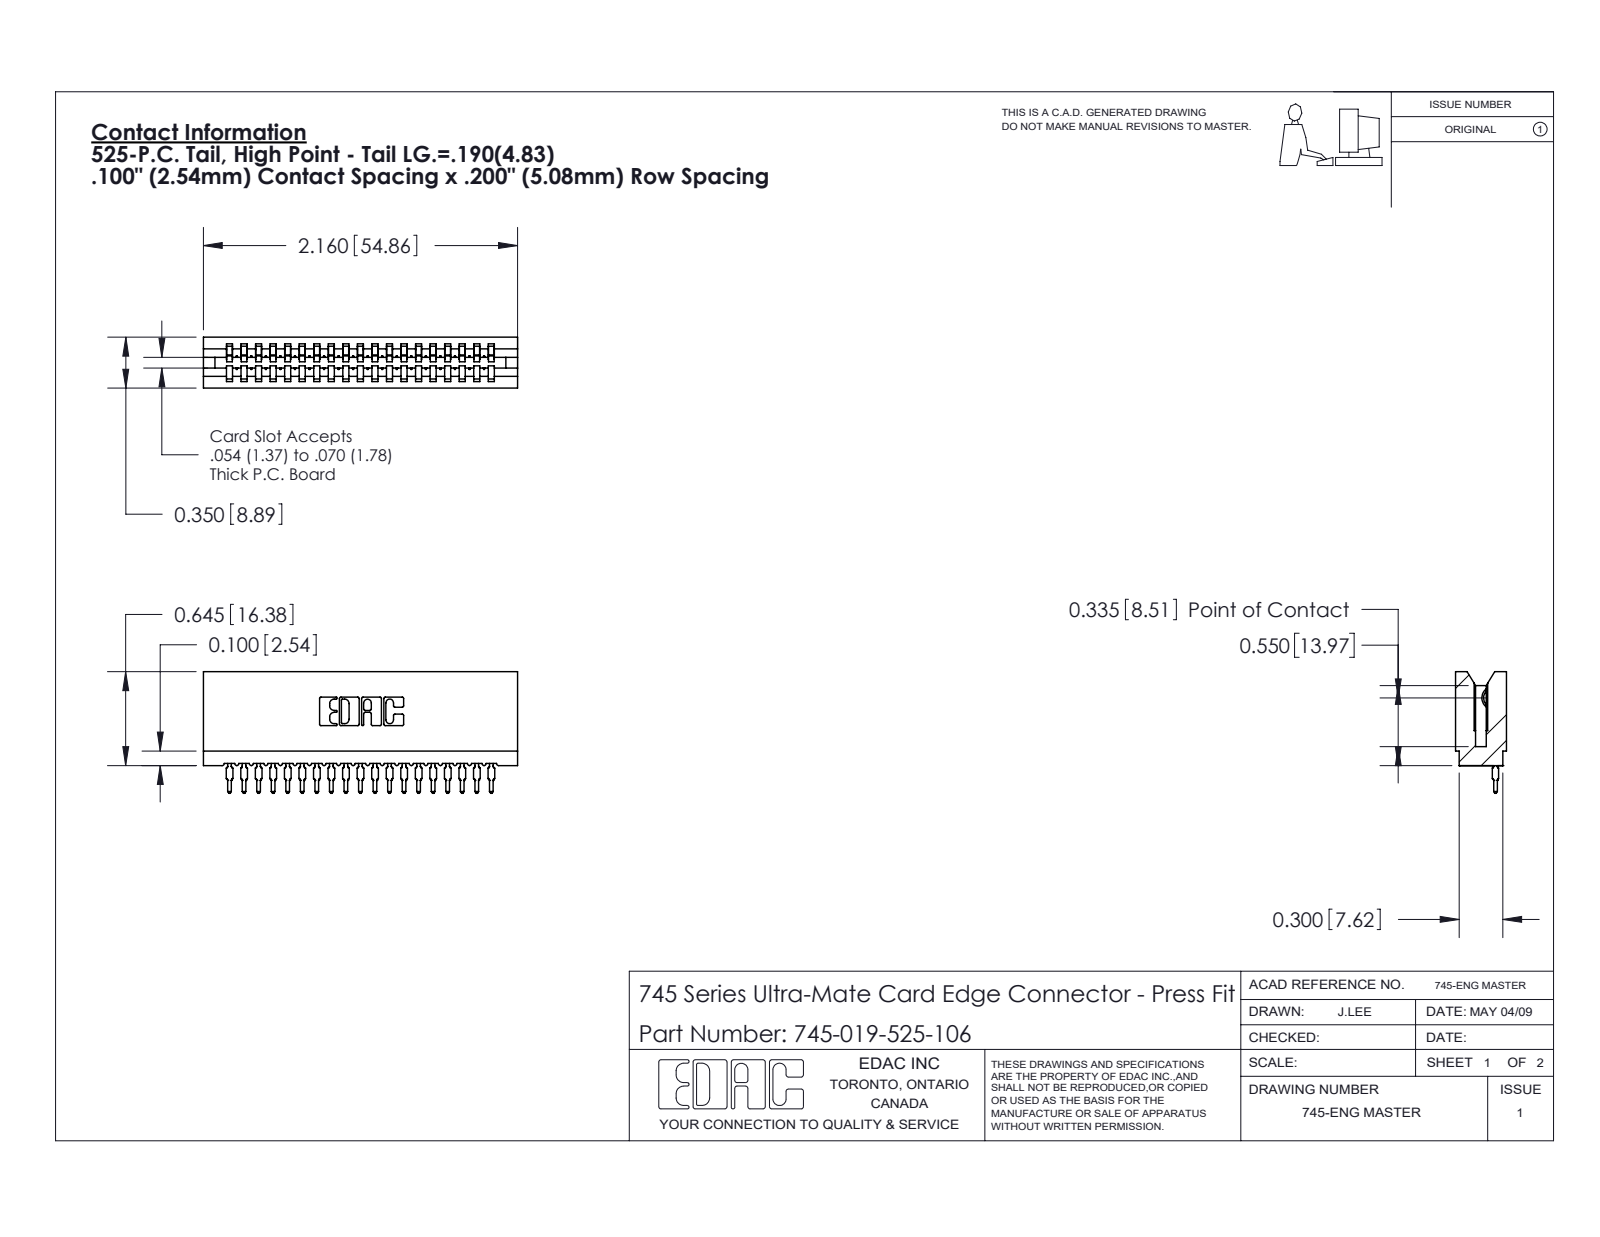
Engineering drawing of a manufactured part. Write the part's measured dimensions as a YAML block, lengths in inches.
part_name: "745-292-001_525; 745-019-525-106; 745 Part_Insulator Option - 06"
step_written_by: "SolidWorks 2020 (CONFIG_CONTROL_DESIGN)"
units: inches
bodies: {solids: 20, faces: 2224, planar: 1329, cylindrical: 401, other: 494}
overall_size: [2.16, 0.836, 0.35]
volume: 0.297
surface_area: 13.33
partial_cylinders:
  - {radius: 0.015, count: 38}
  - {radius: 0.021, count: 38}
  - {radius: 0.01, count: 22}
  - {radius: 0.007, count: 6}
  - {radius: 0.031, count: 6}
  - {radius: 0.005, count: 4}
  - {radius: 0.011, count: 4}
  - {radius: 0.026, count: 3}
face_to_face_distances: [0.1, 0.2, 0.35, 0.5, 0.4, 0.138, 0.212, 0.6, 0.3, 0.045]
